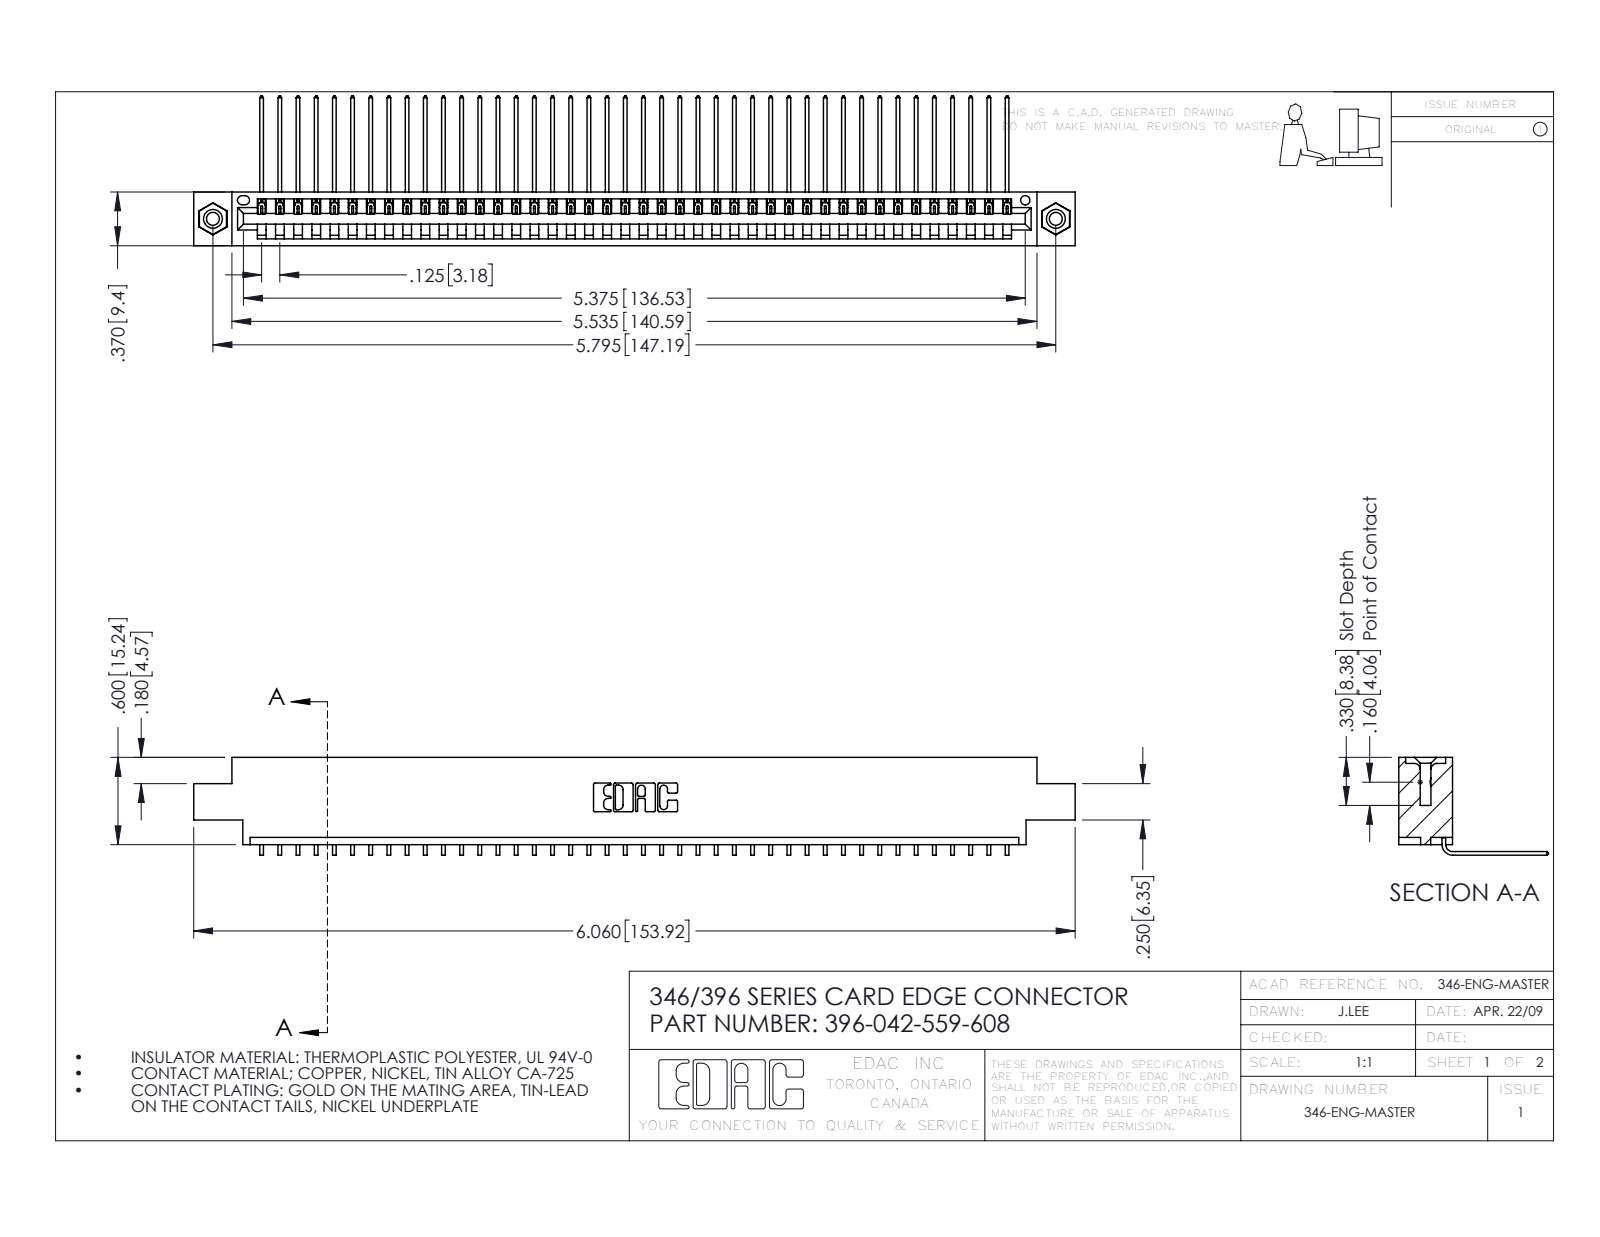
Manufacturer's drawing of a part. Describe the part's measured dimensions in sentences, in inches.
The part is named "345-292-001_558 559 Tail - 1; 345-250-001_345-250-003-102; 346 Part_0.170 Offset - 0.156 Dia-TI; 396-042-559-608". Its 3-D file was written by "SolidWorks 2016 (CONFIG_CONTROL_DESIGN)". It is 45 solids with 2706 faces: 1876 planar, 814 cylindrical and 16 other. Overall it measures 6.06 by 1.03 by 0.673 inches. Its volume is 0.898 cubic inches and its surface area 30.08 square inches. Round holes: 2 of diameter 0.089, 2 of diameter 0.125, 2 of diameter 0.156, 1 of diameter 0.064. Round bosses or shafts: 2 of diameter 0.155. Partial cylindrical surfaces (rounded edges, fillets, slot ends): 84 of radius 0.006, 22 of radius 0.01, 6 of radius 0.007, 6 of radius 0.031, 3 of radius 0.026, 2 of radius 0.031, 2 of radius 0.04, 1 of radius 0.014. The main face-to-face distances are 0.048, 0.322, 0.37, 0.025, 0.25, 0.072, 0.222, 0.148, 0.298, 0.1. The hole center spacings are 0.246, 5.586, 5.795.
